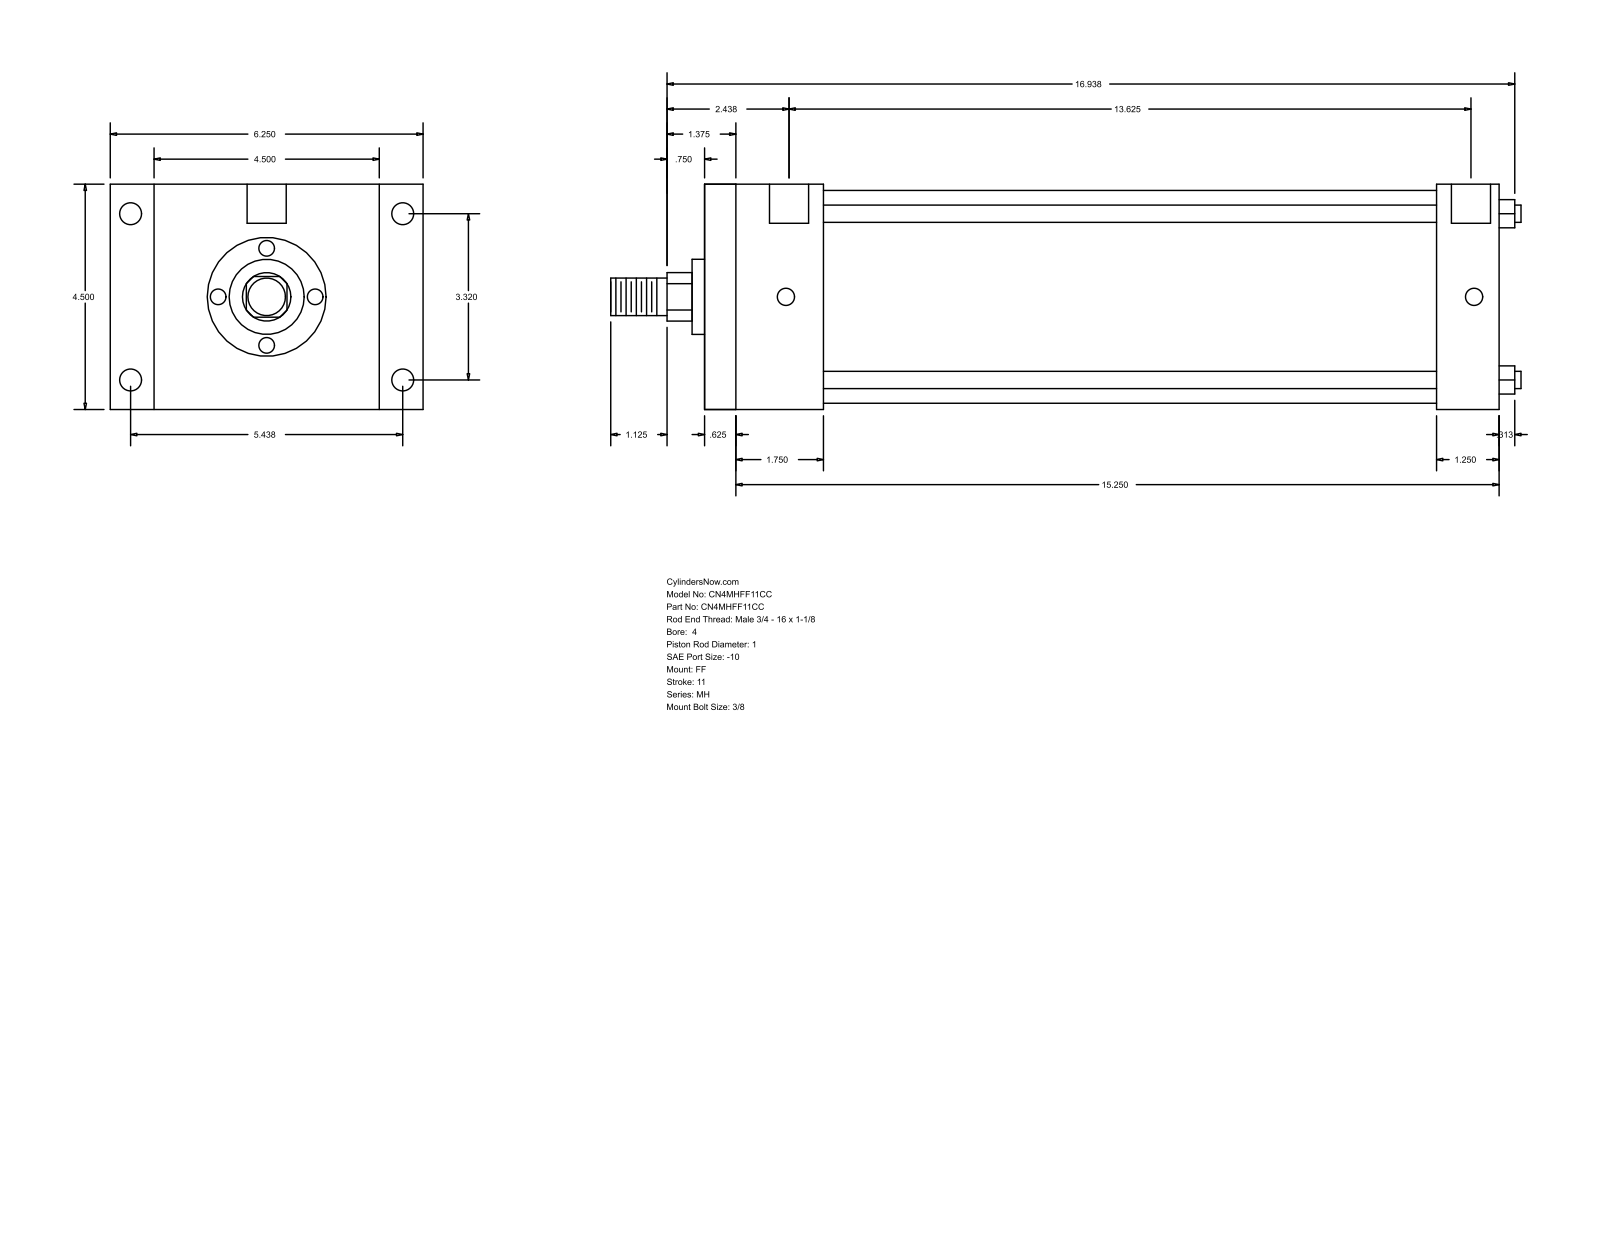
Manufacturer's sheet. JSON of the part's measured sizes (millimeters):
{"part_name": "MH_FF__0400_1", "step_written_by": "GSSL Pune (CONFIG_CONTROL_DESIGN)", "units": "millimeters", "bodies": {"solids": 0, "faces": 92, "planar": 64, "cylindrical": 28, "other": 0}, "overall_size": [461.96, 158.75, 114.3], "round_holes": [[8.73, 4], [11.13, 4], [19.84, 2]], "round_bosses_or_shafts": [[8.76, 4], [107.95, 1], [38.1, 1], [25.4, 1], [19.05, 1]], "partial_cylinders_radius": [[12.29, 1]], "face_to_face_distances": [114.3, 403.22, 15.87, 387.35, 60.33, 44.46, 342.89, 371.47, 355.6, 311.14], "hole_center_spacings": [1.58, 84.32, 138.12, 161.82, 347.66, 349.24, 346.08]}
